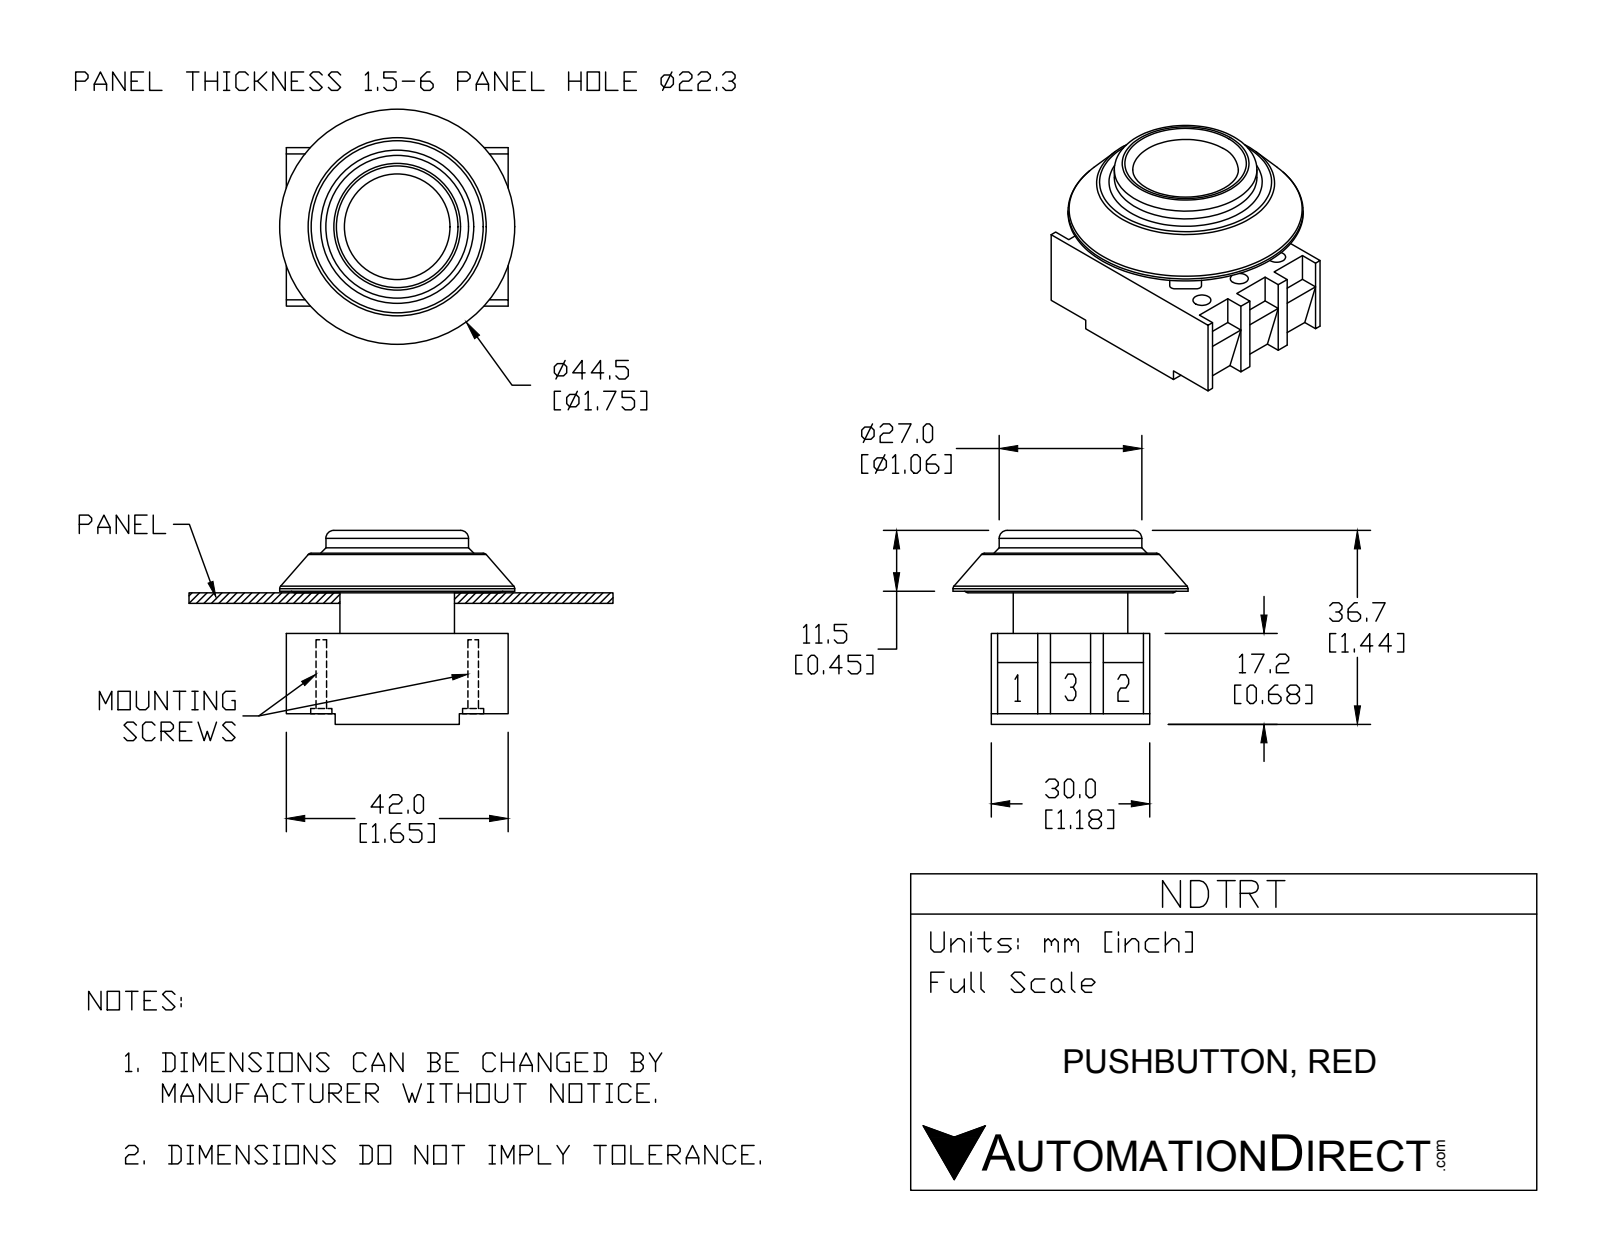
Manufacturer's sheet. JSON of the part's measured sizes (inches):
{"part_name": "NDTRT", "step_written_by": "SolidWorks 2015 (AUTOMOTIVE_DESIGN)", "units": "inches", "bodies": {"solids": 7, "faces": 217, "planar": 127, "cylindrical": 65, "other": 25}, "overall_size": [1.752, 1.752, 1.445], "volume_in3": 1.533, "surface_area_in2": 25.91, "round_holes": [[0.134, 6], [0.197, 6], [0.492, 1]], "round_bosses_or_shafts": [[0.181, 2], [0.157, 2], [1.752, 1], [1.063, 1], [0.854, 1]], "partial_cylinders_radius": [[0.039, 8], [0.343, 5], [0.433, 1]], "face_to_face_distances": [0.283, 0.598, 1.181, 0.394, 0.315, 0.295, 0.303, 0.406, 0.709, 0.913], "hole_center_spacings": [0.394, 0.69, 1.199, 1.132, 0.566, 0.787, 1.379]}
